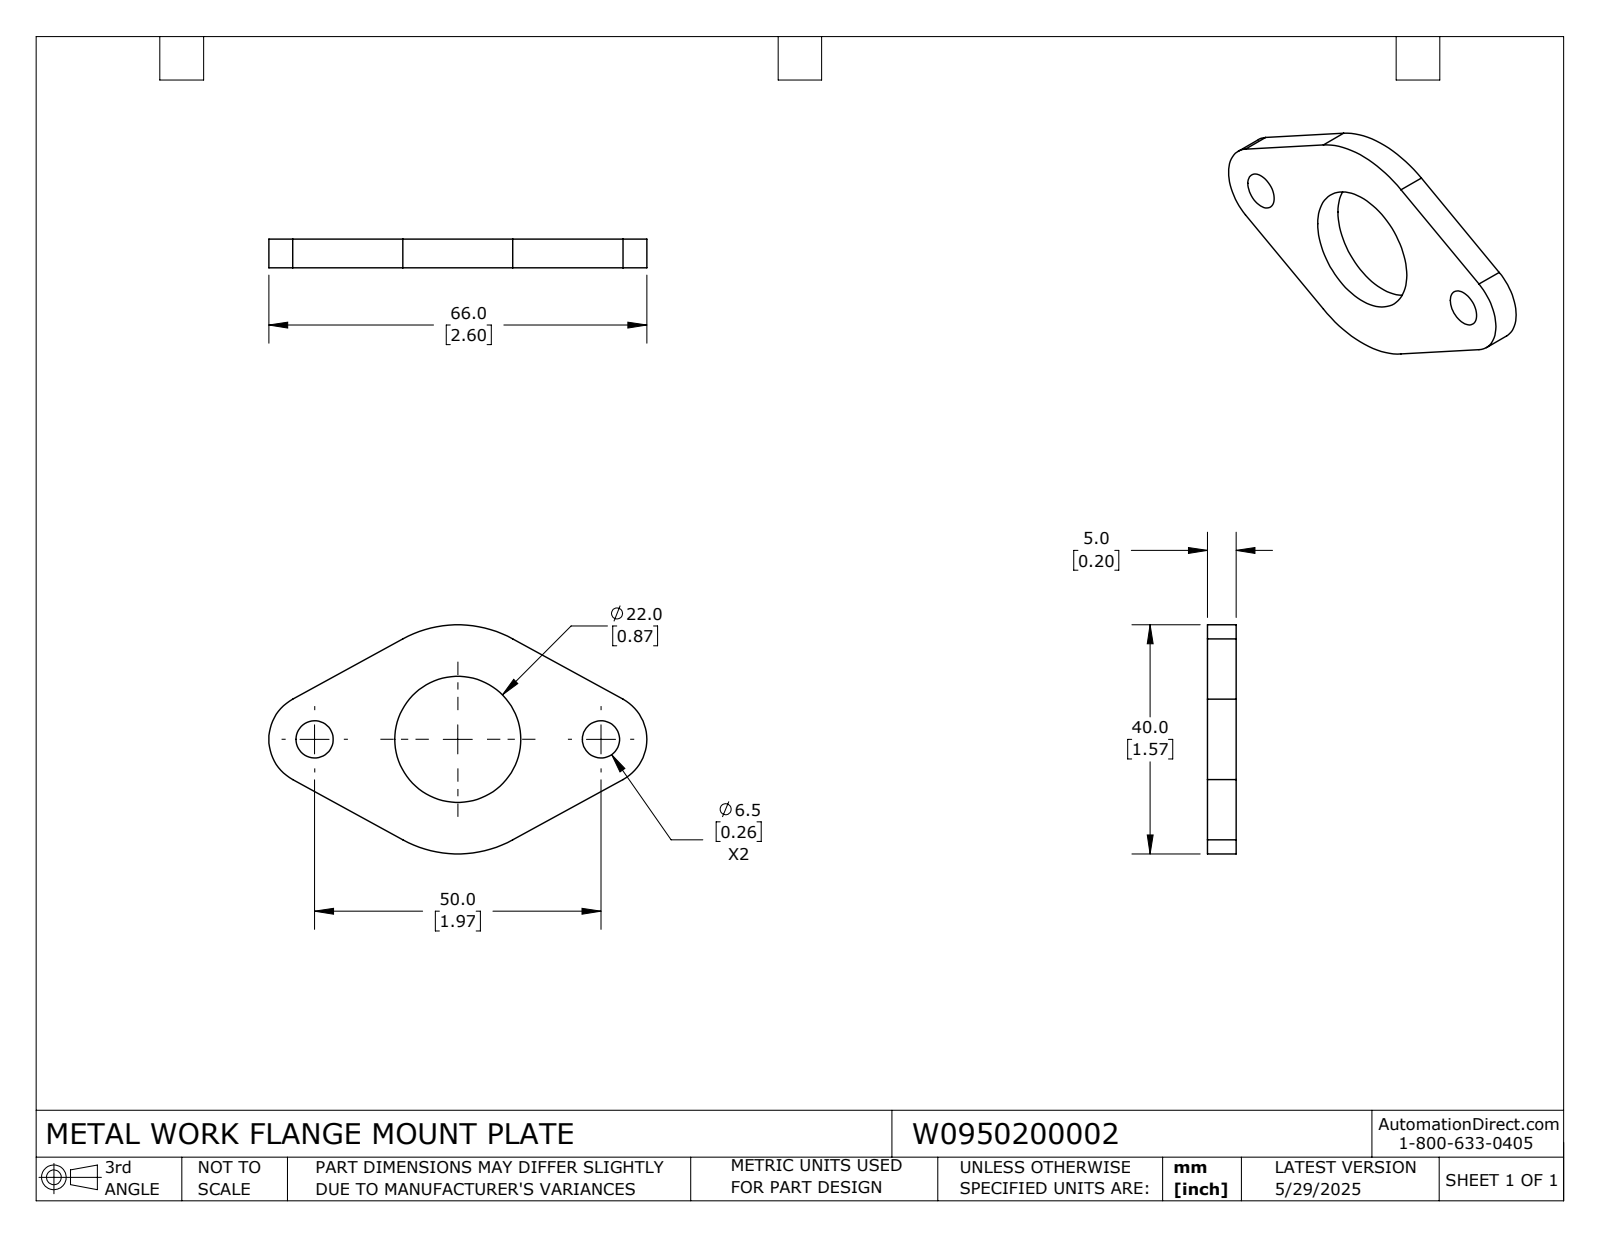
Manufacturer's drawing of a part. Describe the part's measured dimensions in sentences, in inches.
The part is named "W0950200002". Its 3-D file was written by "SolidWorks 2024 (CONFIG_CONTROL_DESIGN)". It is 1 solid with 17 faces: 6 planar, 11 cylindrical and 0 other. Overall it measures 2.598 by 1.575 by 0.197 inches. Its volume is 0.403 cubic inches and its surface area 6.197 square inches. Round holes: 2 of diameter 0.256, 1 of diameter 0.866. Partial cylindrical surfaces (rounded edges, fillets, slot ends): 2 of radius 0.315, 1 of radius 0.787. The main face-to-face distances are 0.197, 1.575. The hole center spacings are 0.984, 1.969.
